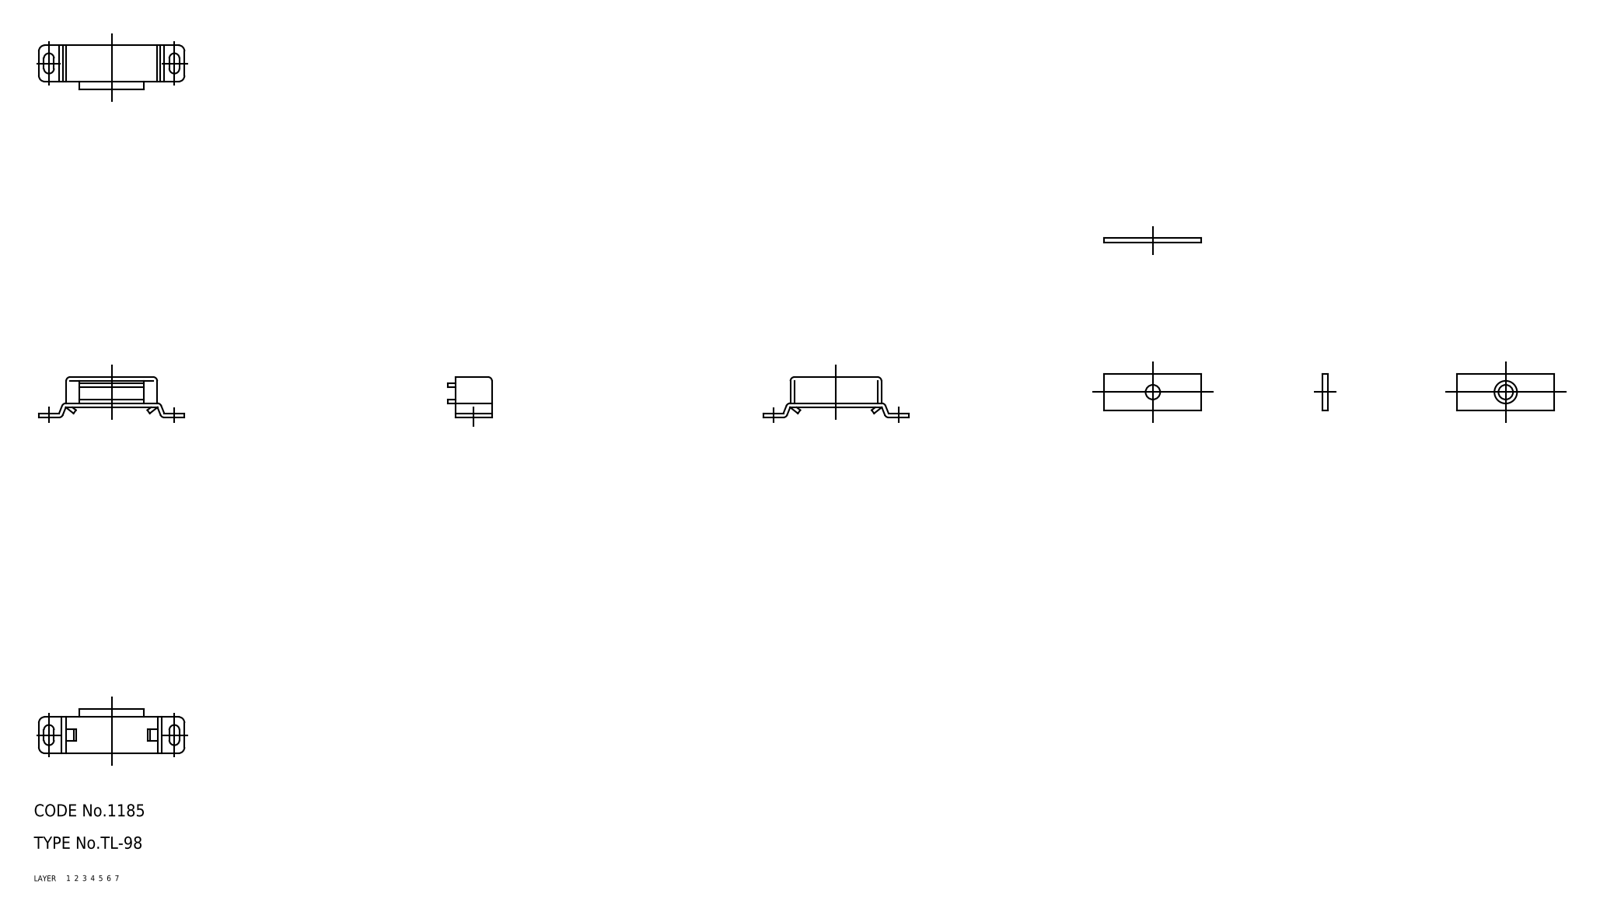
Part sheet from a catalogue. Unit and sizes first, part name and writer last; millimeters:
Units: millimetres
Overall size (bounding box): 36 × 21.2 × 10.75
Volume: 1 499 mm³ · Surface area: 3 171 mm²
Bodies: 6 solids, 113 faces (0 planar, 0 cylindrical, 113 other)
Part name (STEP PRODUCT): attachment; magnet; keeper; housing (+2 more)
STEP written by: CADfix (AUTOMOTIVE_DESIGN)
